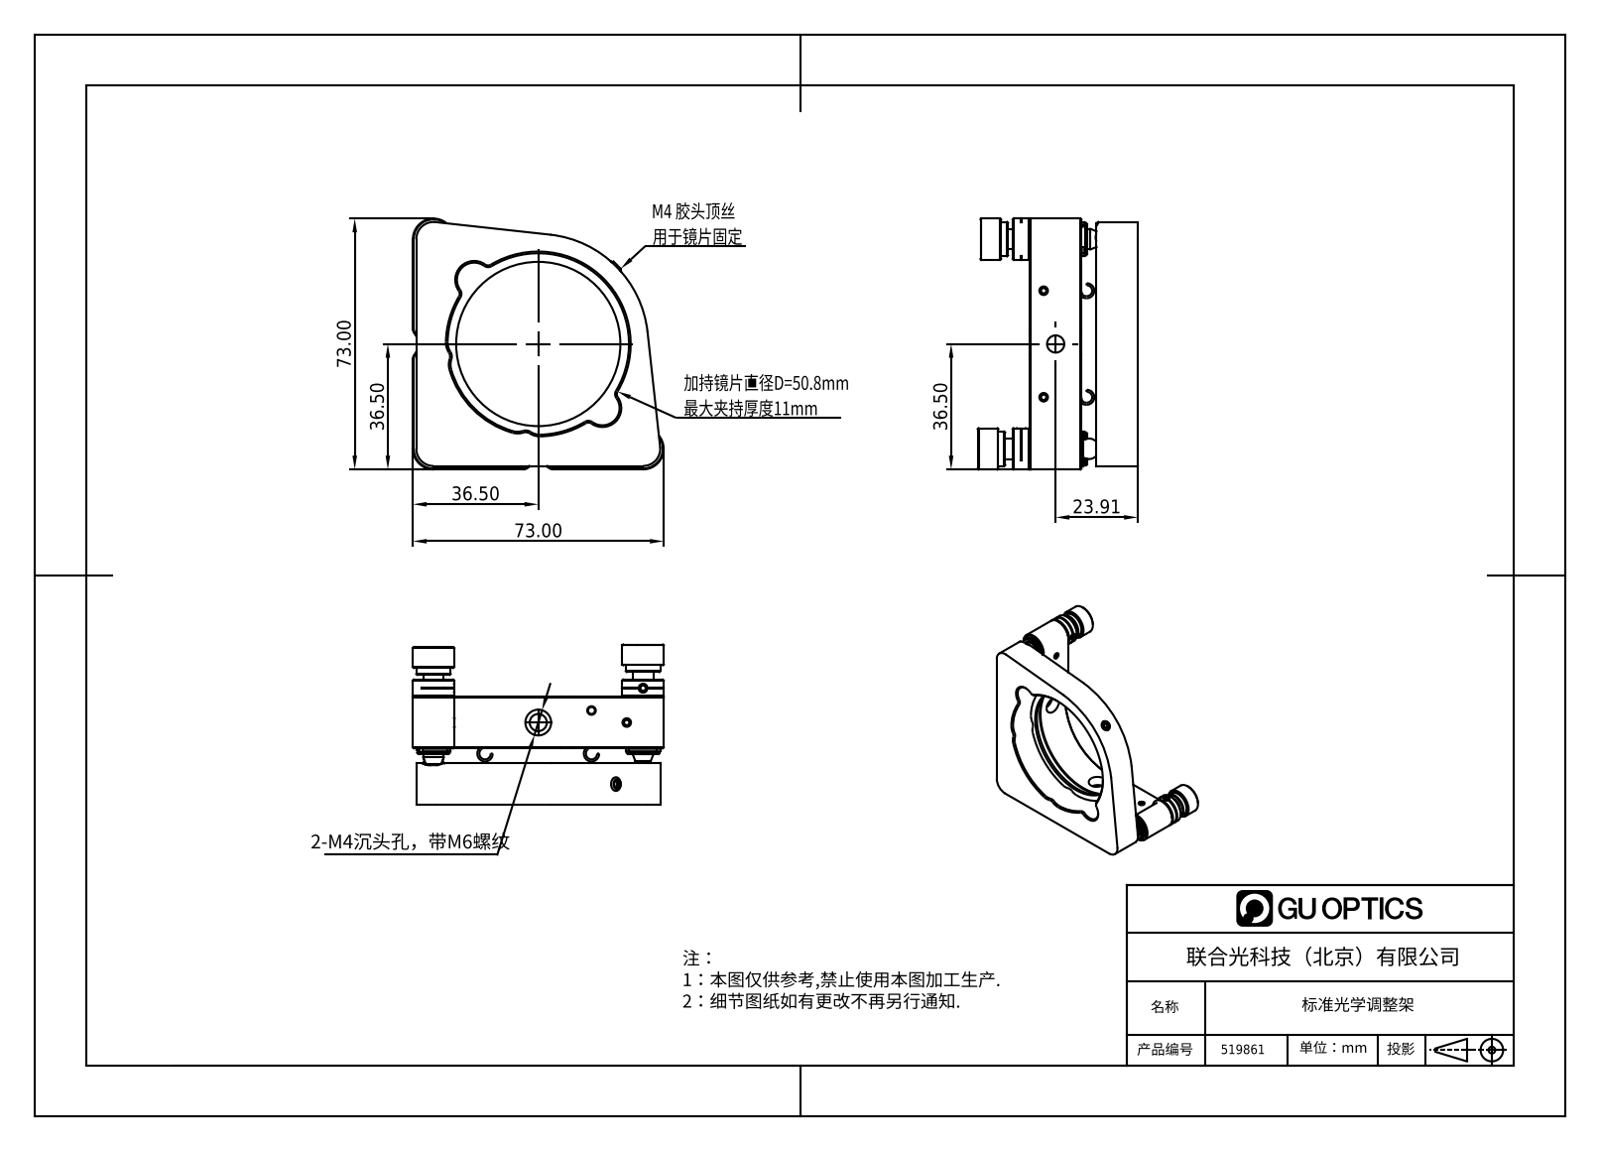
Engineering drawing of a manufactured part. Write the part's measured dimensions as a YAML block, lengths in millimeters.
part_name: "30.8.8-14，M4尼龙头顶丝，A_30.8.9-LNJ4*5; 36.1，440c不锈钢滚珠_36.1.8_GZ-B6; DXS-0625标准型六角调节器 _3.2.2.17.1-DXS-0625-31.6; 30.5.1-14，LPJ3，M3不锈钢平头紧定螺丝_30.5.1-LPJ3*3 (+8 more)"
step_written_by: "SolidWorks 2021 (CONFIG_CONTROL_DESIGN)"
units: millimeters
bodies: {solids: 31, faces: 746, planar: 206, cylindrical: 243, other: 297}
overall_size: [73, 73, 46.6]
volume: 50711
surface_area: 29019
round_holes:
  - {diameter: 2.5, count: 9}
  - {diameter: 6, count: 6}
  - {diameter: 3.3, count: 5}
  - {diameter: 5, count: 3}
  - {diameter: 3.99, count: 2}
  - {diameter: 4, count: 2}
  - {diameter: 6.5, count: 2}
  - {diameter: 7.5, count: 2}
  - {diameter: 2, count: 1}
  - {diameter: 9.5, count: 1}
  - {diameter: 47.8, count: 1}
round_bosses_or_shafts:
  - {diameter: 3, count: 10}
  - {diameter: 10, count: 3}
  - {diameter: 4, count: 3}
  - {diameter: 12, count: 2}
  - {diameter: 9.5, count: 2}
  - {diameter: 8, count: 2}
  - {diameter: 8.9, count: 1}
partial_cylinders:
  - {radius: 0.2, count: 24}
  - {radius: 2, count: 8}
  - {radius: 5, count: 8}
  - {radius: 0.5, count: 4}
  - {radius: 2.5, count: 2}
  - {radius: 4, count: 2}
  - {radius: 10, count: 2}
  - {radius: 6, count: 1}
face_to_face_distances: [12, 1, 31.4, 19.4, 4.4, 16.4, 15, 11, 5.4, 20.4]
hole_center_spacings: [15, 15.89, 31, 34.21, 46, 10.83, 25.75, 41.4]
